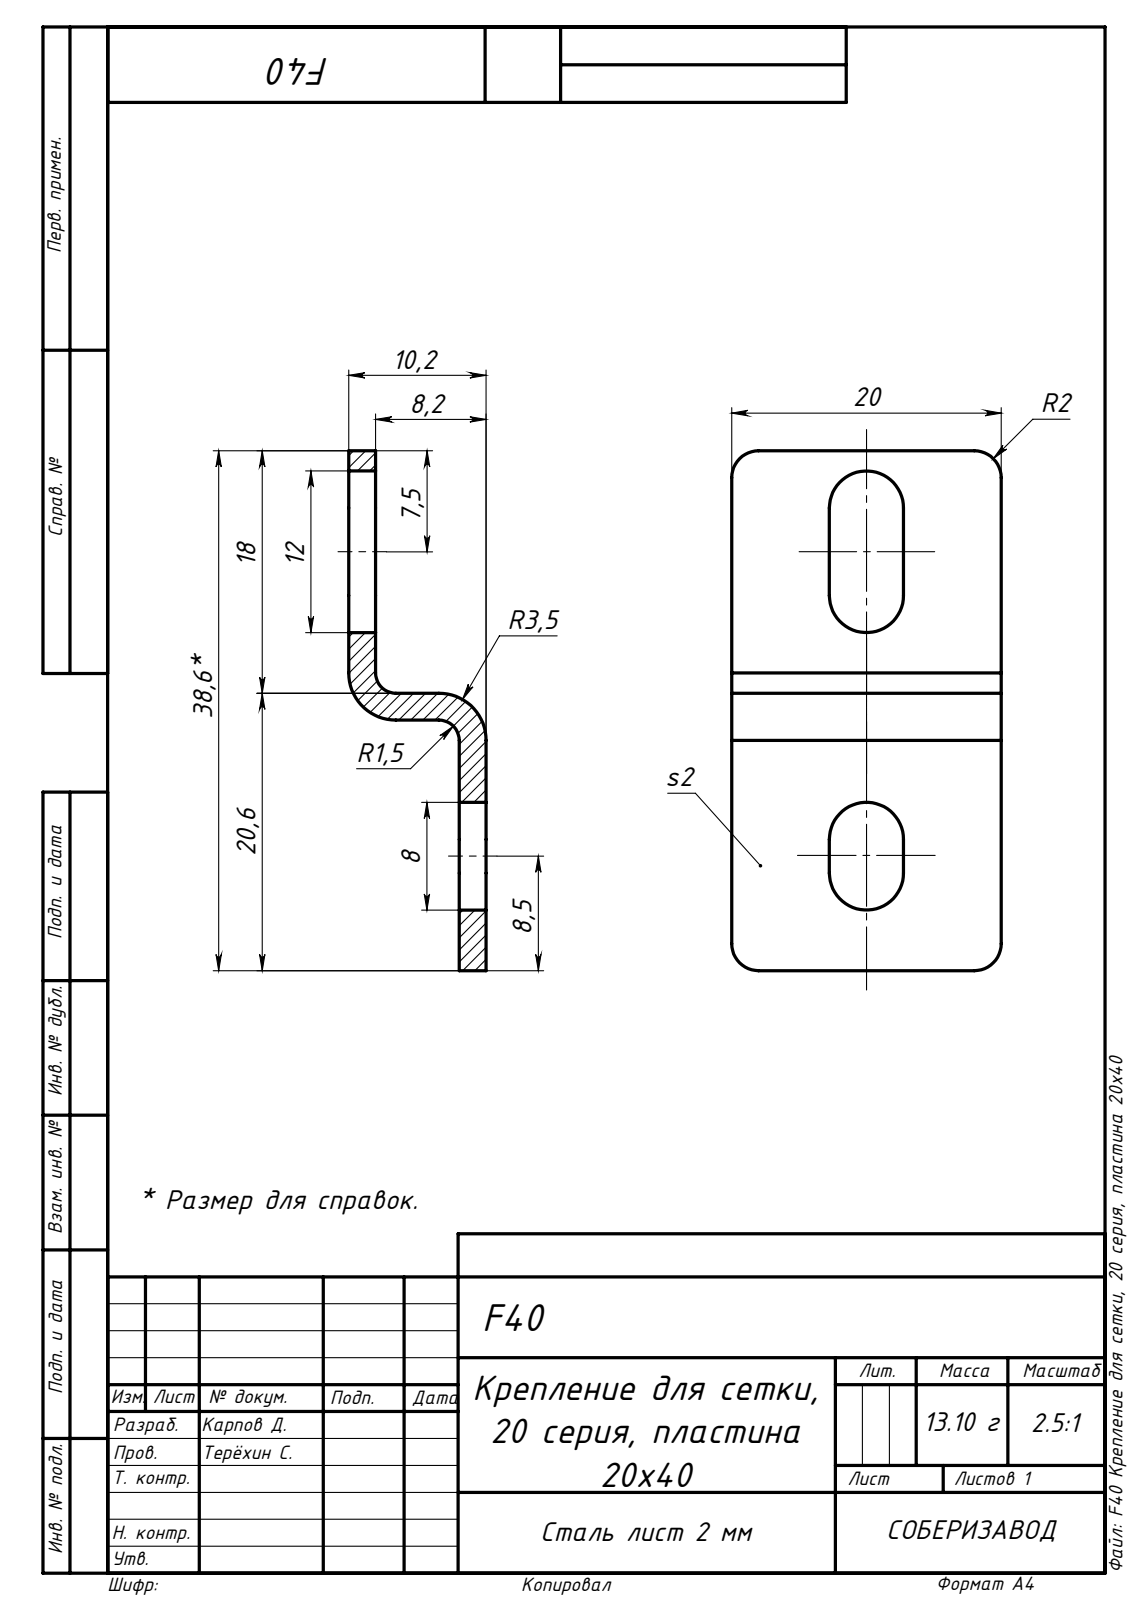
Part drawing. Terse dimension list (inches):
name: F40 Крепление для сетки, 20 серия, пластина 20х40
written by: SolidWorks 2019 (AUTOMOTIVE_DESIGN)
unit: in
bodies: 1 solid, 36 faces (22 planar, 14 cylindrical, 0 other)
size: 1.52 × 0.787 × 0.402
volume: 0.097 in³; area: 3.01 in²
rounds: 4× R0.079, 4× R0.108, 2× R0.059, 2× R0.138
face distances: 0.079, 0.323, 0.244, 0.402, 0.787, 0.285, 0.502, 0.732, 0.811, 1.52
